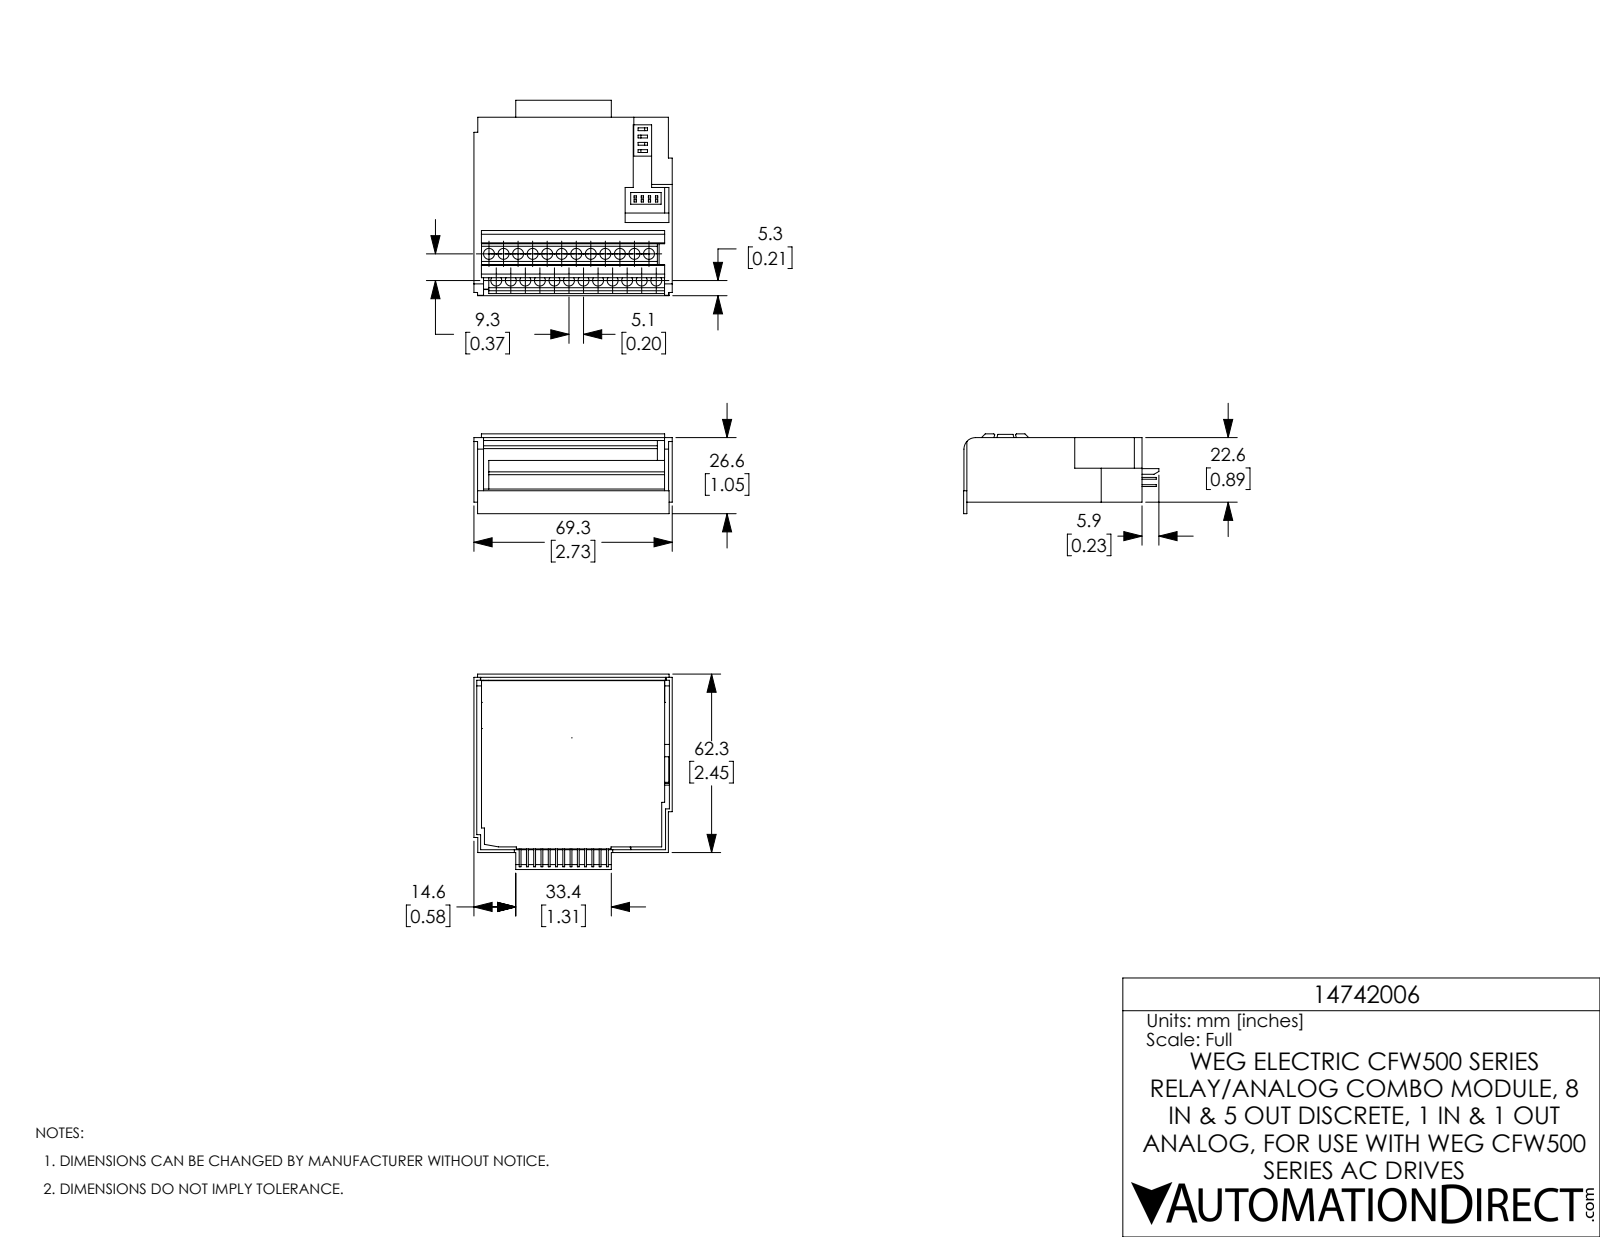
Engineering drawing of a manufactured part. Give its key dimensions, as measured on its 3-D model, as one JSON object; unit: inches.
{"part_name": "14742006_CJ MODULO IO CFW500_IOD Coord nc", "step_written_by": "SolidWorks 2017 (AUTOMOTIVE_DESIGN)", "units": "inches", "bodies": {"solids": 1, "faces": 437, "planar": 385, "cylindrical": 52, "other": 0}, "overall_size": [2.726, 2.685, 1.096], "volume_in3": 1.904, "surface_area_in2": 46.68, "round_holes": [[0.15, 24]], "partial_cylinders_radius": [[0.118, 1], [0.157, 1]], "face_to_face_distances": [0.039, 0.73, 0.063, 0.667, 0.77, 0.707, 2.687, 2.727, 0.051, 1.704], "hole_center_spacings": [0.38, 0.2, 0.474, 0.4, 0.62, 0.6, 0.79, 0.8]}
